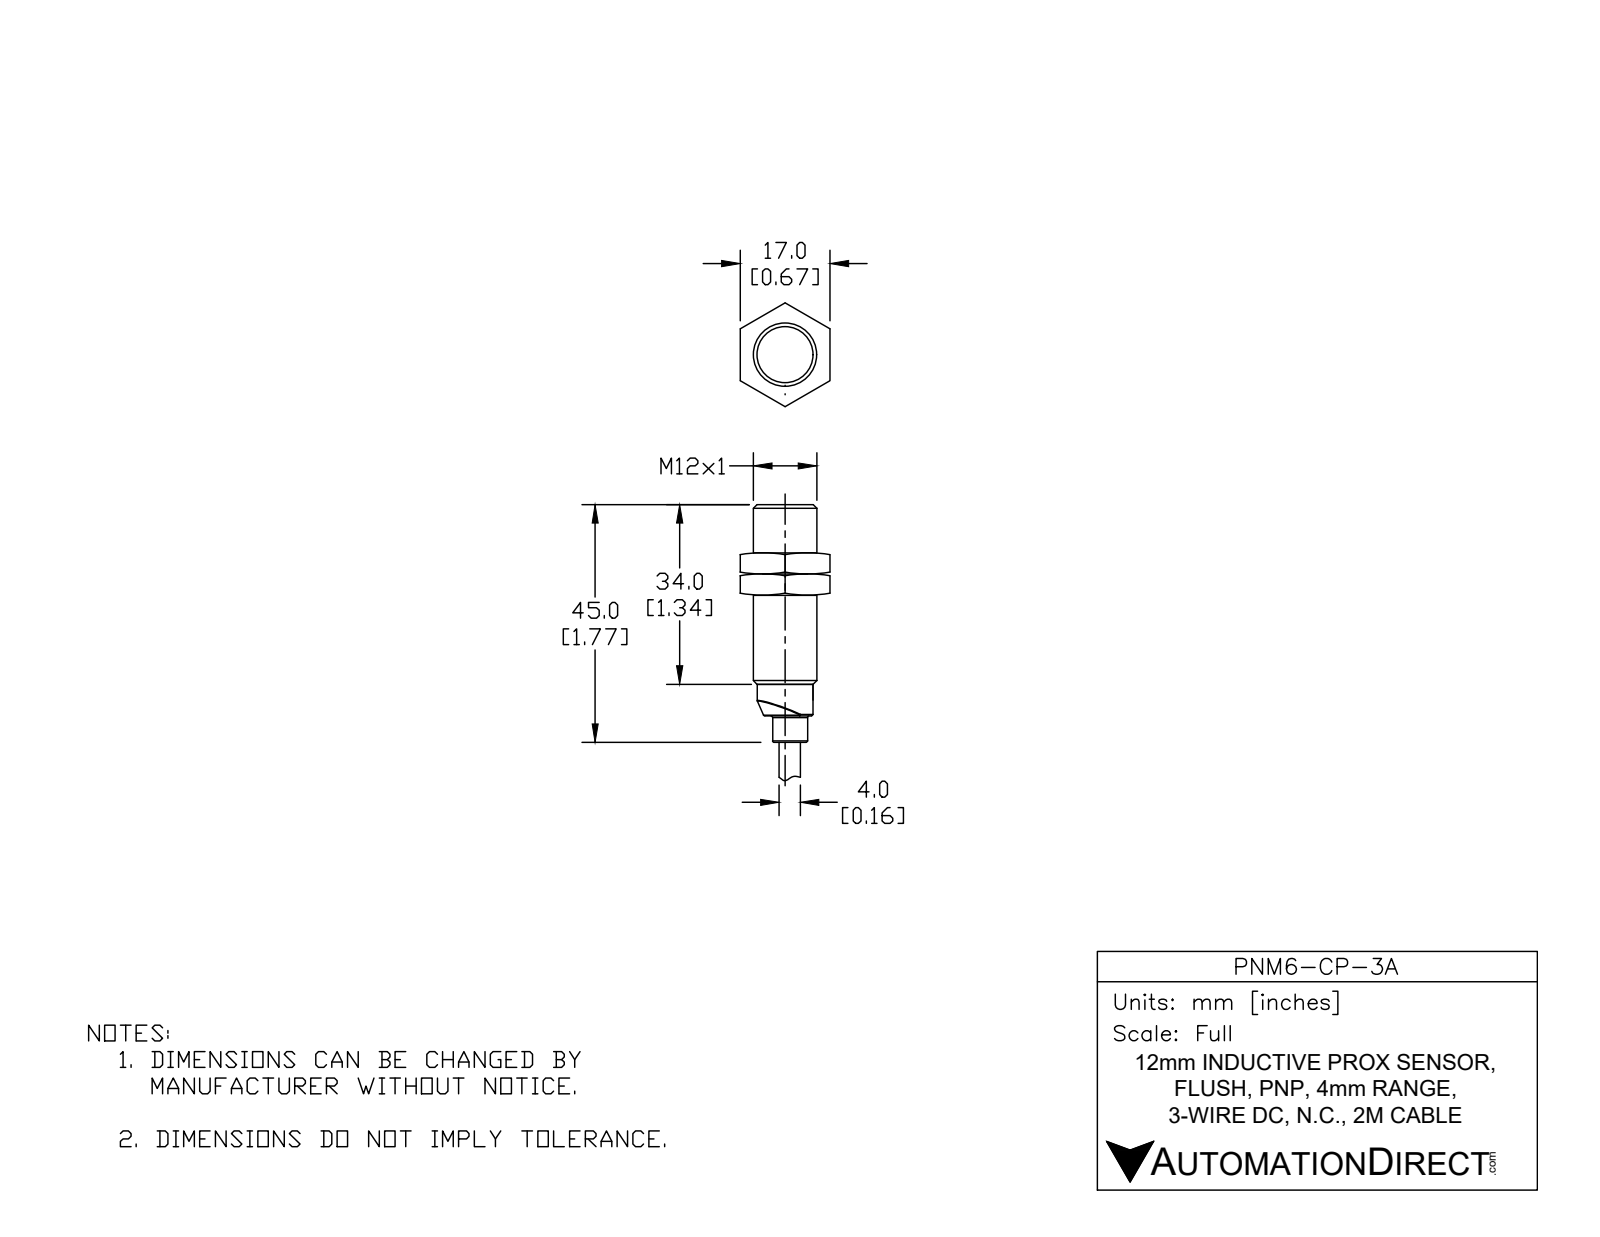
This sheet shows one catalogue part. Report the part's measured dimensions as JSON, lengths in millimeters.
{"part_name": "PNM6-CP-3A", "step_written_by": "SolidWorks 2017 (AUTOMOTIVE_DESIGN)", "units": "millimeters", "bodies": {"solids": 1, "faces": 59, "planar": 13, "cylindrical": 23, "other": 23}, "overall_size": [95.8, 12, 12], "volume_mm3": 5130, "surface_area_mm2": 2606, "round_holes": [[4.1, 1]], "round_bosses_or_shafts": [[1.2, 3], [12, 1], [10.6, 1], [10.5, 1], [6.6, 1], [4, 1]], "partial_cylinders_radius": [[0.6, 1], [2, 1]], "face_to_face_distances": [40, 45, 5, 95.8, 55.8, 50.8, 37, 3, 8, 58.8]}
